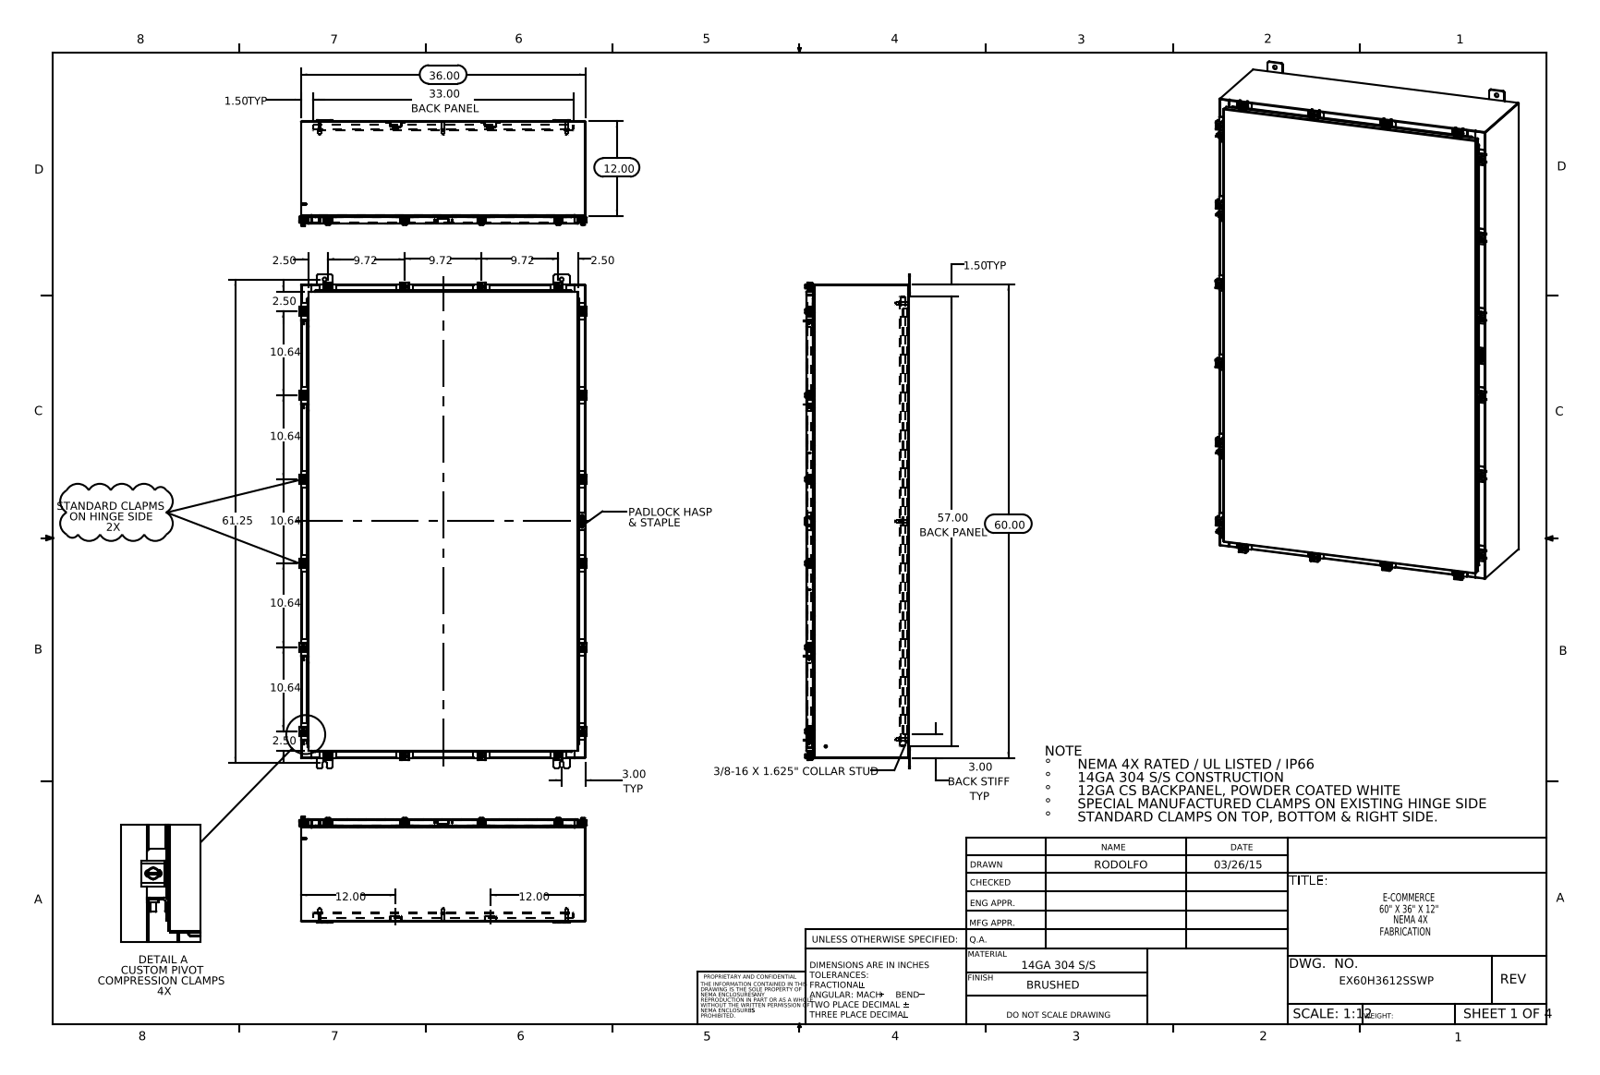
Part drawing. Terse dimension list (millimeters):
name: EX60H3612SSWP Mounting Studs; Clamp Top_RTP31; N-WMT04X30402202210-00 22101002; EX60H3612SSWP (+8 more)
written by: SolidWorks 2014 (CONFIG_CONTROL_DESIGN)
unit: mm
bodies: 140 solids, 3424 faces (1773 planar, 1319 cylindrical, 332 other)
size: 1587.5 × 925.1 × 341.7
volume: 12 990 000 mm³; area: 12 700 000 mm²
holes: 20× ⌀5.4, 20× ⌀6.6, 12× ⌀12.7, 9× ⌀6.4, 1× ⌀3.2
bosses: 20× ⌀12.7, 20× ⌀6.4, 16× ⌀10.1, 8× ⌀15.9, 8× ⌀9.5, 8× ⌀8.4, 8× ⌀4, 8× ⌀3.6
rounds: 84× R1.5, 40× R3.6, 38× R0.3, 36× R3, 34× R2.2, 32× R2.3, 29× R1.3, 28× R3.7
face distances: 1.9, 327.7, 325.8, 2.6, 329.6, 25.4, 27.3, 300.4, 302.3, 29.9
hole spacings: 50, 56.5, 59.6, 354.9, 374.1, 409.6, 701.7, 755.5
